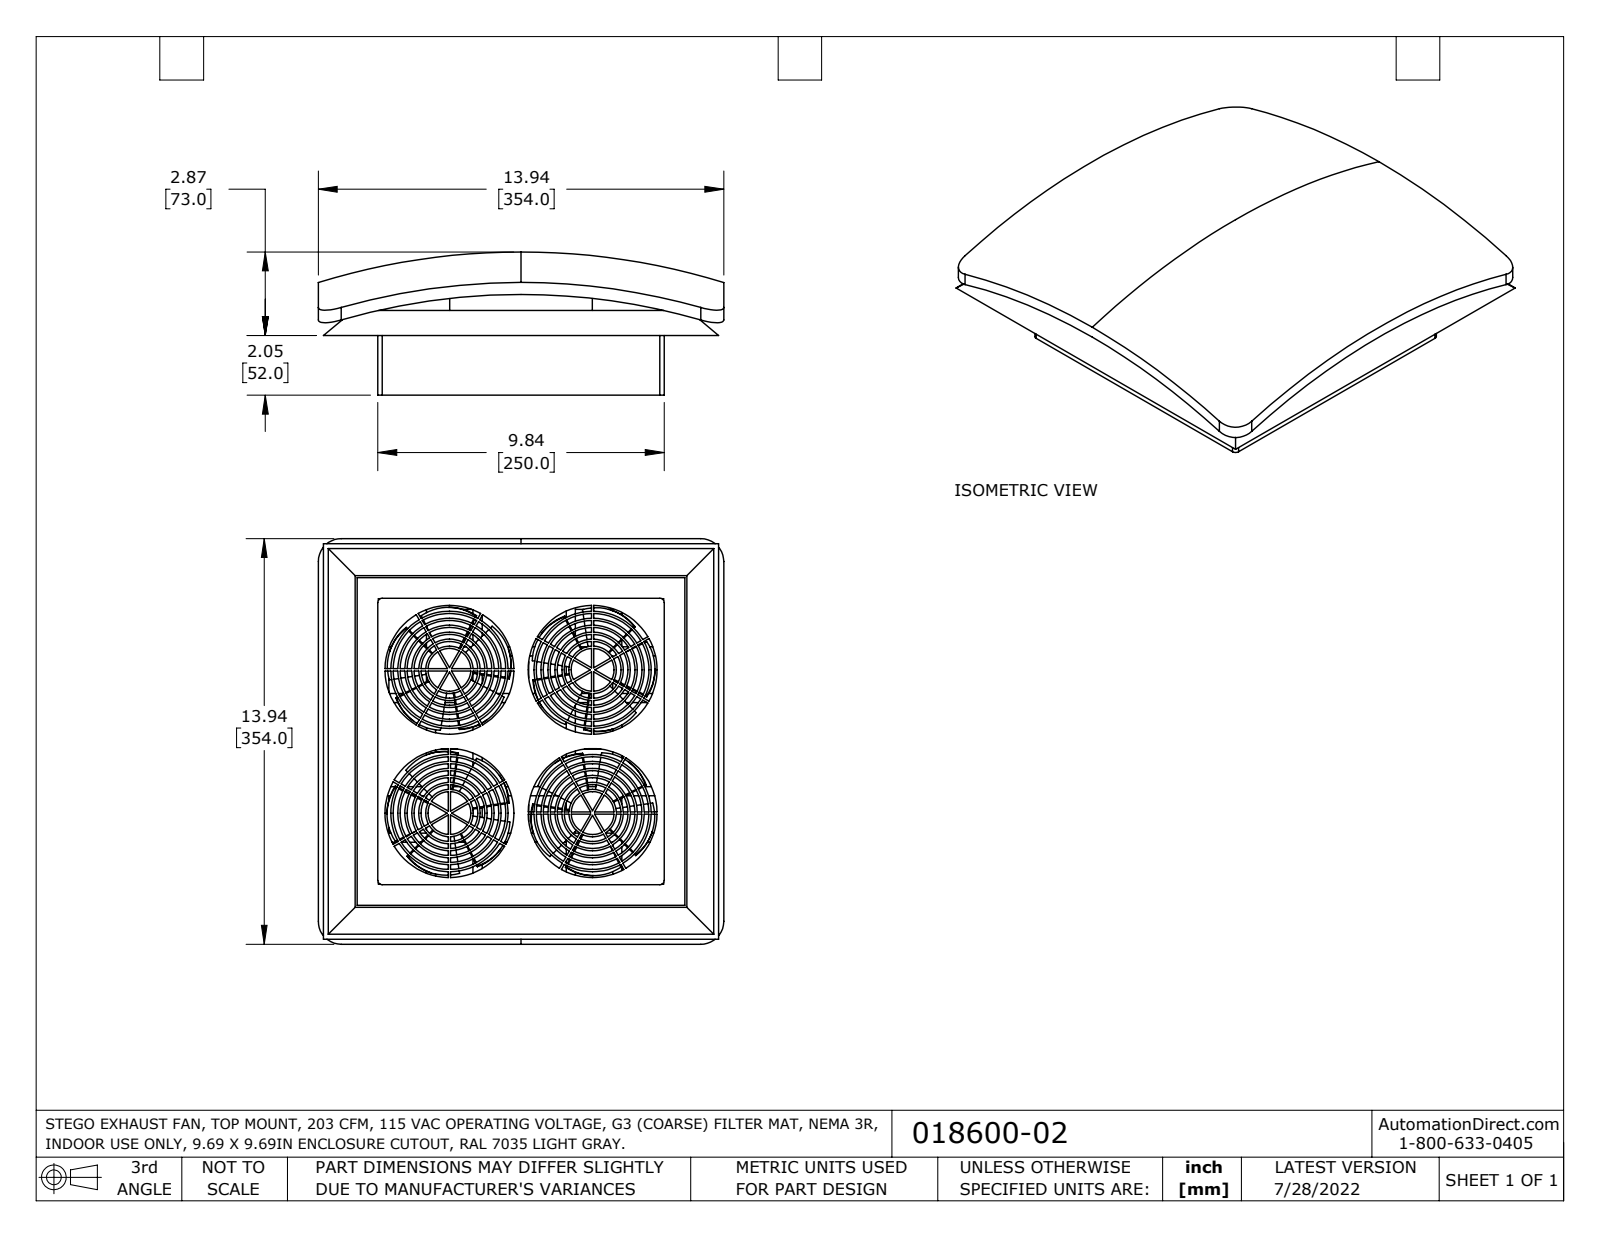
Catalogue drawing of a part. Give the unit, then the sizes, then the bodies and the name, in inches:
Units: inches
Overall size (bounding box): 13.937 × 13.937 × 4.921
Round holes (diameter × count): ⌀1.471 ×4, ⌀1.951 ×4, ⌀2.431 ×4, ⌀2.911 ×4, ⌀3.391 ×4, ⌀3.871 ×4, ⌀4.429 ×4
Round bosses / shafts (diameter × count): ⌀4.028 ×4, ⌀3.068 ×4, ⌀2.589 ×4, ⌀2.109 ×4, ⌀1.629 ×4, ⌀1.55 ×4, ⌀3.548 ×2, ⌀3.548 ×2
Partial cylindrical surfaces — rounded edges, fillets, slot ends (radius × count): R2.148 ×12, R2.148 ×8, R0.148 ×4, R0.787 ×4
Main face-to-face distances: 0.431, 0.862, 2.047, 0.109, 2.478, 2.909, 0.079, 9.843, 2.22, 0.172
Hole centre spacings: 4.921, 6.96
Volume: 257.8 in³ · Surface area: 1 407 in²
Bodies: 1 solid, 1107 faces (675 planar, 428 cylindrical, 4 other)
Part name (STEP PRODUCT): 018600-02_Default
STEP written by: SolidWorks 2021 (CONFIG_CONTROL_DESIGN)
